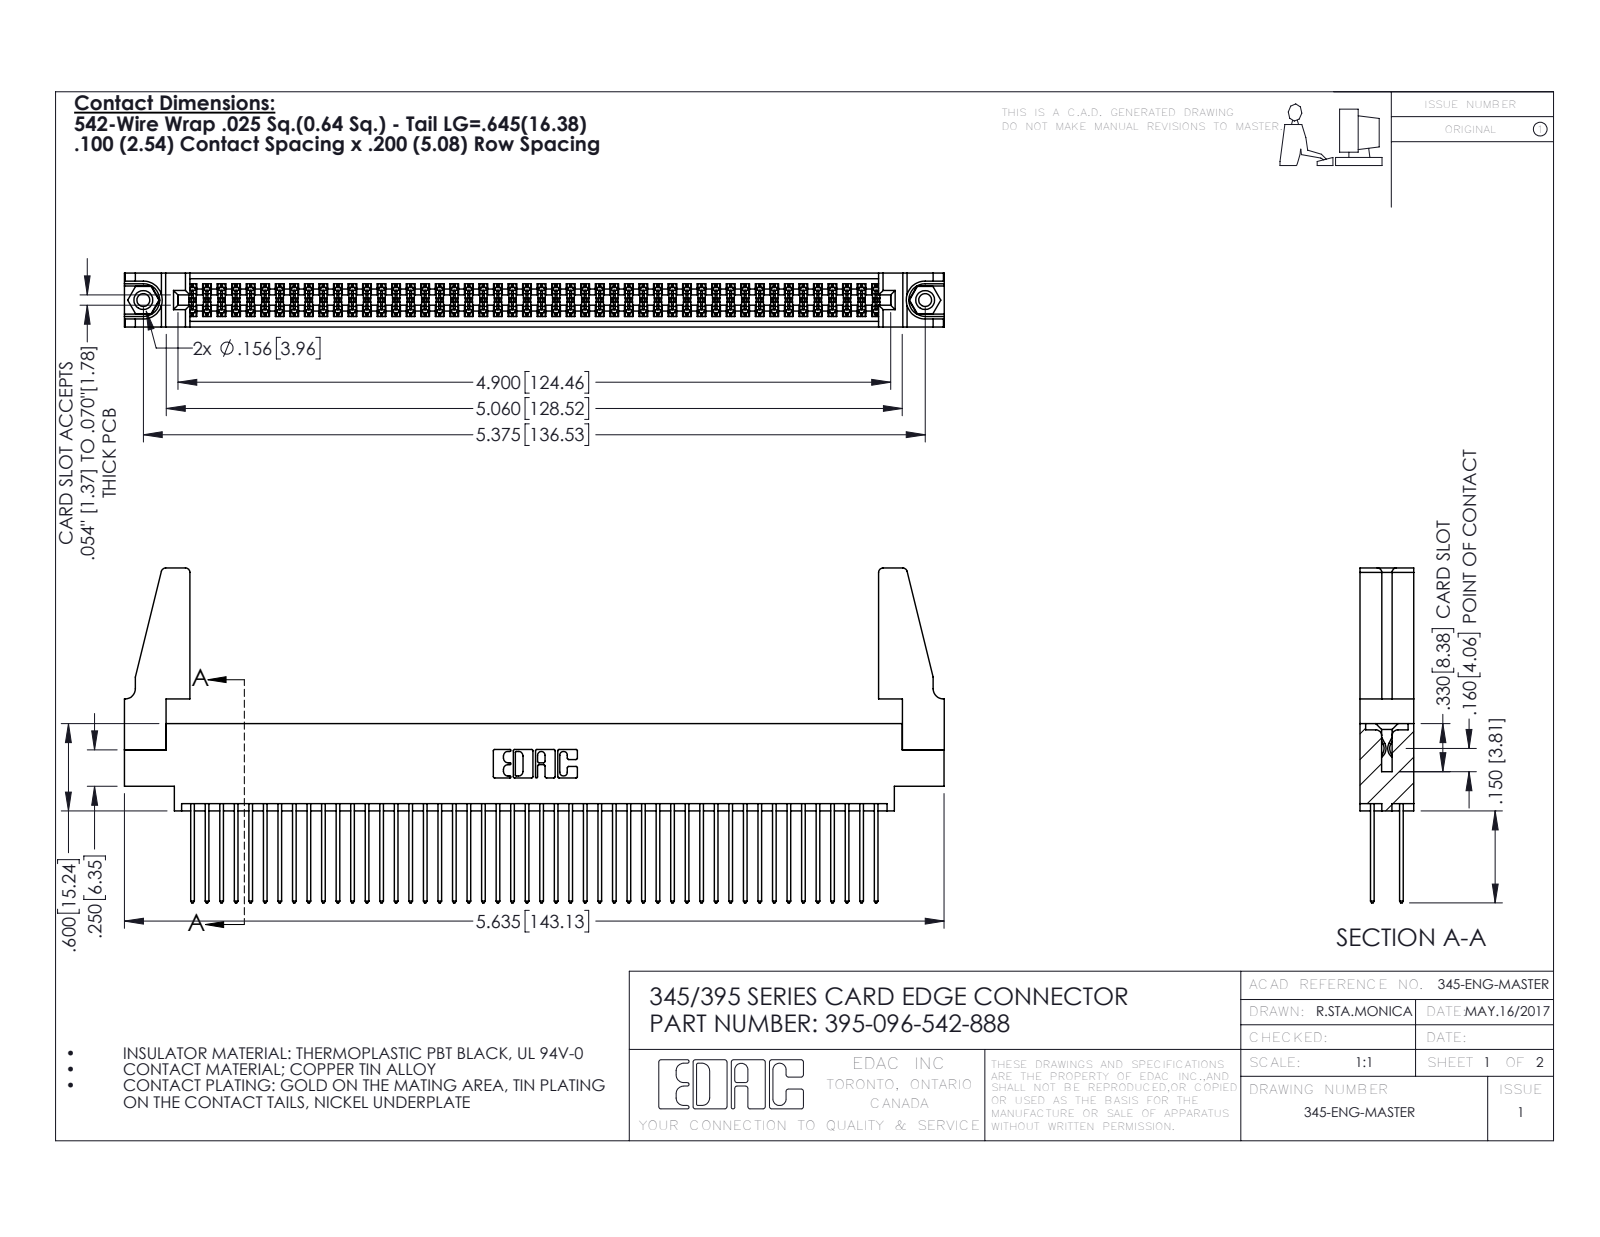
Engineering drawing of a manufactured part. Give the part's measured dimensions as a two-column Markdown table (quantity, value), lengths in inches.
| quantity | value |
| --- | --- |
| part name | 345-220-078_345-220-088; 395-096-542-888; 345-292-001_345-293-142; 345-250-001_345-250-001-102 (+1 more) |
| STEP written by | SolidWorks 2016 (CONFIG_CONTROL_DESIGN) |
| units | inches |
| bodies | 101 solids, 5054 faces (3324 planar, 1714 cylindrical, 16 other) |
| overall size | 5.636 × 2.302 × 0.37 |
| volume | 1.071 in³ |
| surface area | 41.24 in² |
| round holes (diameter × count) | 0.089 × 2, 0.125 × 2, 0.156 × 2, 0.064 × 1 |
| round bosses / shafts (diameter × count) | 0.155 × 2 |
| partial cylindrical surfaces (radius × count) | 0.006 × 144, 0.01 × 96, 0.01 × 22, 0.03 × 8, 0.007 × 6, 0.031 × 6, 0.026 × 3, 0.014 × 2 |
| main face-to-face distances | 0.072, 0.298, 0.098, 0.272, 0.025, 0.2, 0.37, 0.225, 0.175, 0.149 |
| hole center spacings | 0.27, 5.139, 5.375 |
